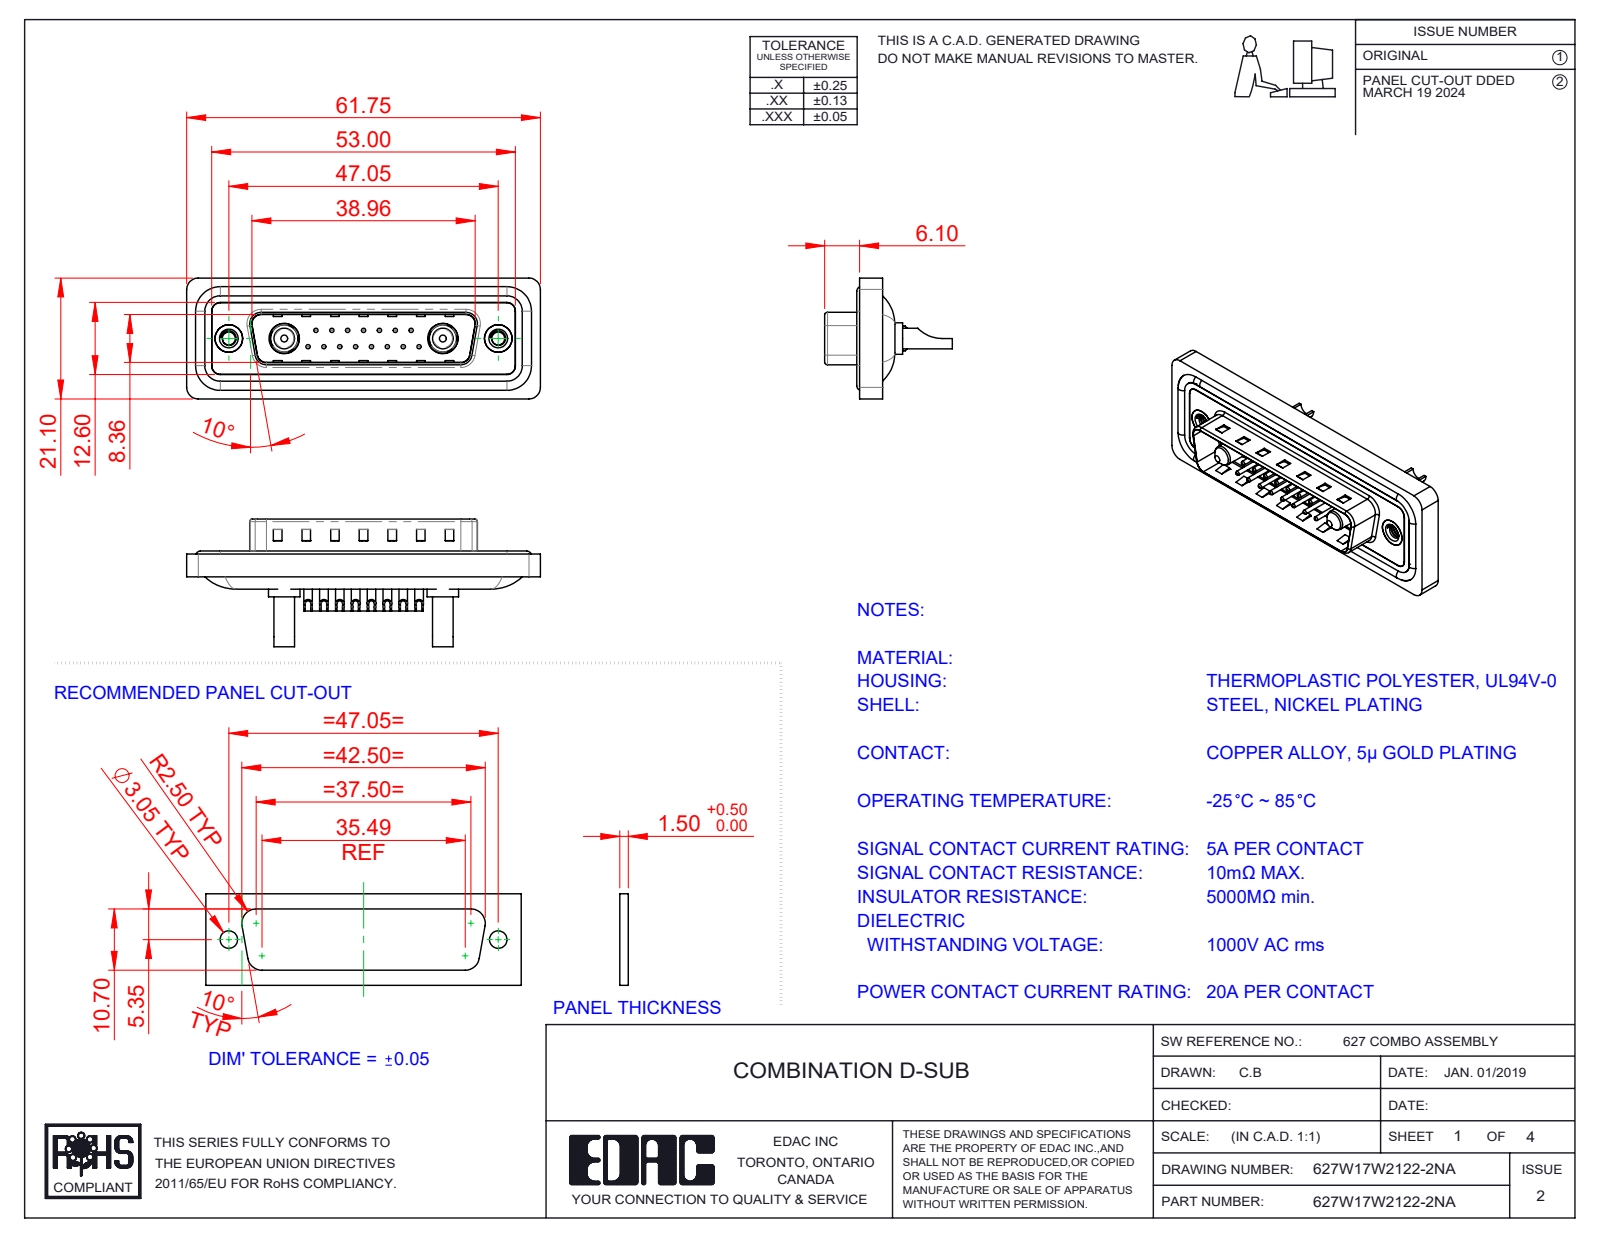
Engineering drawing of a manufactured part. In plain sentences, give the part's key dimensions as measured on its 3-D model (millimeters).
The part is named "627Combo Housing_17W2; 627Combo Waterproof Housing_25 Contacts; 627Combo Threaded Rivet_A; Power Pin_20A SC (+5 more)". Its 3-D file was written by "SolidWorks 2023 (CONFIG_CONTROL_DESIGN)". It is 26 solids with 1126 faces: 370 planar, 474 cylindrical and 282 other. Overall it measures 61.75 by 22.3 by 21.1 millimeters. Its volume is 7 317 cubic millimeters and its surface area 12 196 square millimeters. Round holes: 15 of diameter 0.75, 15 of diameter 1, 15 of diameter 1.6, 15 of diameter 2, 2 of diameter 2.26, 2 of diameter 2.7, 2 of diameter 4, 2 of diameter 4.8, 2 of diameter 4.85, 2 of diameter 5, 2 of diameter 5.3. Round bosses or shafts: 15 of diameter 1.5, 4 of diameter 1.6, 2 of diameter 5.5, 2 of diameter 5.2, 2 of diameter 4.9, 2 of diameter 4.75, 2 of diameter 3.75, 2 of diameter 3.6. Partial cylindrical surfaces (rounded edges, fillets, slot ends): 22 of radius 1.5, 18 of radius 2, 8 of radius 0.5, 8 of radius 1.6, 6 of radius 1, 4 of radius 0.25, 4 of radius 0.6, 4 of radius 0.65. The main face-to-face distances are 0.4, 1.5, 1.1, 1.6, 0.5, 3.1, 2.9, 0.82, 9.58, 4.1. The hole center spacings are 3.16, 2.77, 5.54, 8.31, 5.04, 7.49, 11.08, 5.03.
